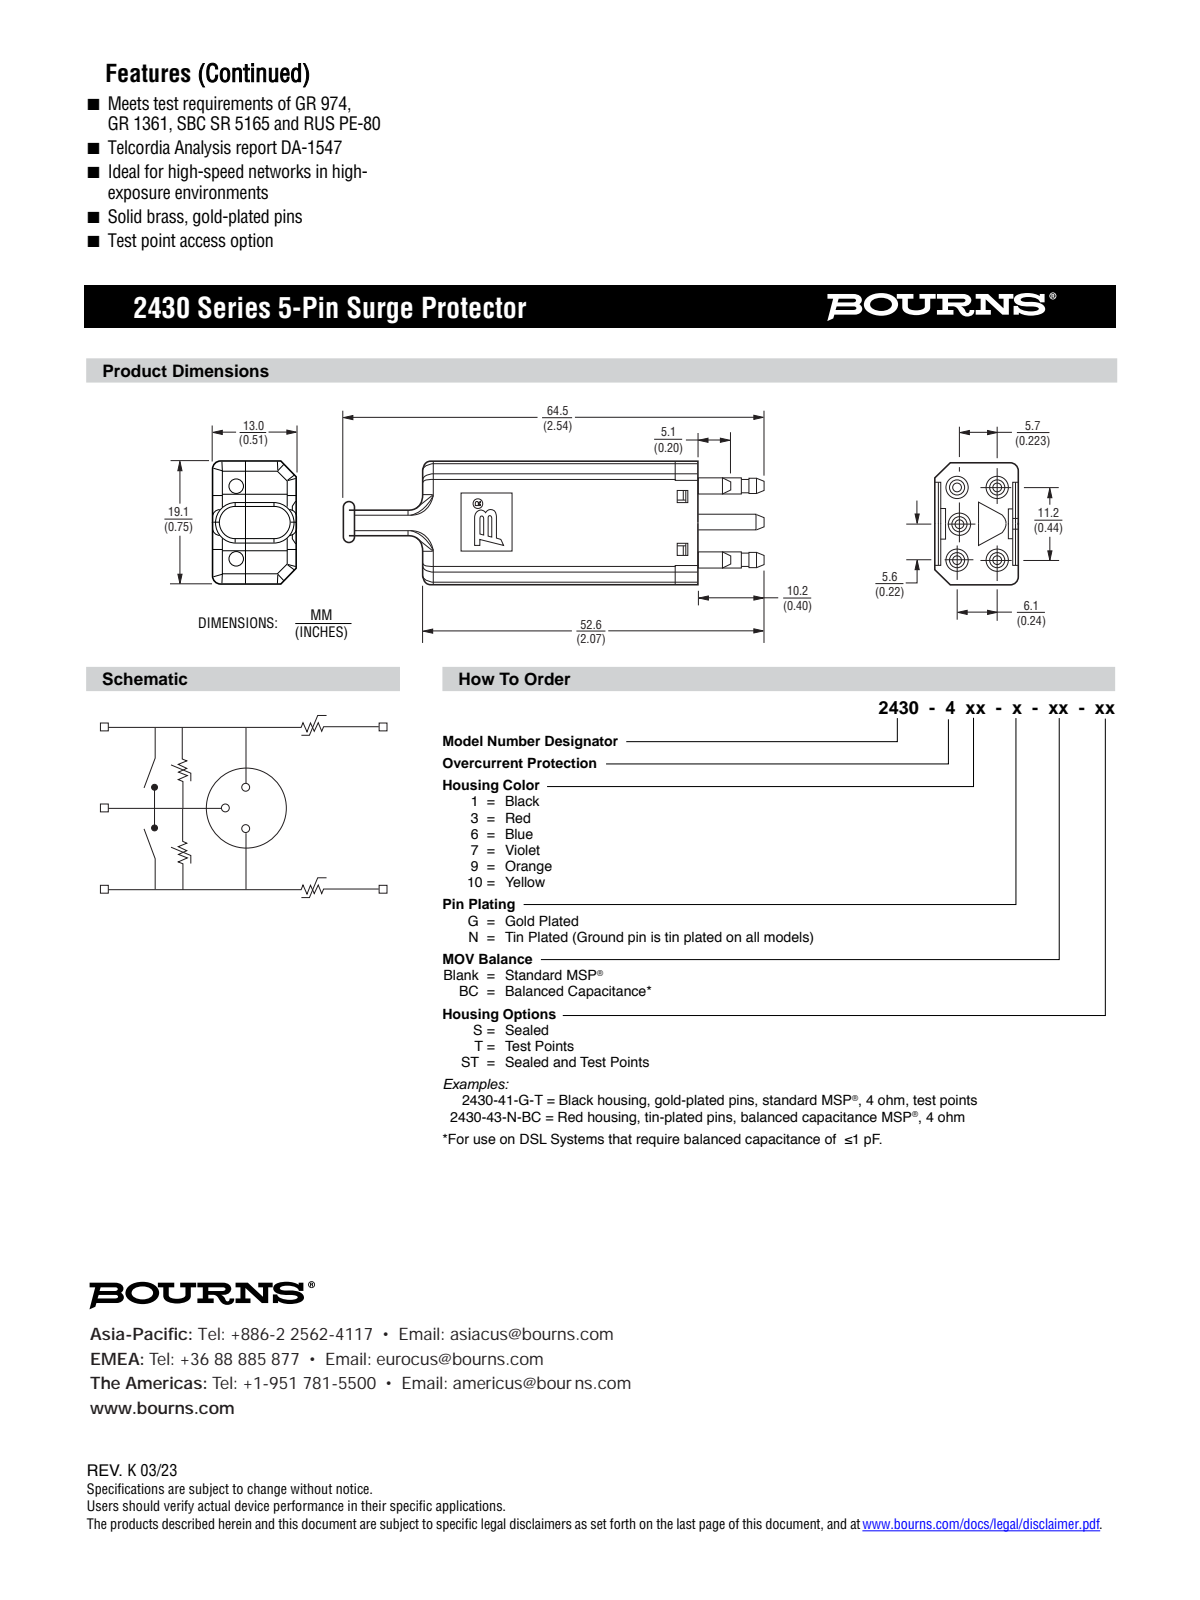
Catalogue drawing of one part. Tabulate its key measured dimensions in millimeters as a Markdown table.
| quantity | value |
| --- | --- |
| part name | 2440 |
| STEP written by | PRO/ENGINEER BY PARAMETRIC TECHNOLOGY CORPORATION, 2010100 (CONFIG_CONTROL_DESIGN) |
| units | millimeters |
| bodies | 1 solid, 93 faces (27 planar, 42 cylindrical, 24 other) |
| overall size | 64.5 × 19.1 × 13 |
| volume | 11 165 mm³ |
| surface area | 3 810 mm² |
| round holes (diameter × count) | 2.2 × 2 |
| round bosses / shafts (diameter × count) | 2.3 × 5 |
| partial cylindrical surfaces (radius × count) | 0.5 × 16, 0.4 × 6, 3 × 4 |
| main face-to-face distances | 13, 19.1, 7.5, 11.6, 42.4, 4.1, 11.9, 54.3, 2, 6.47 |
| hole center spacings | 11.2 |
